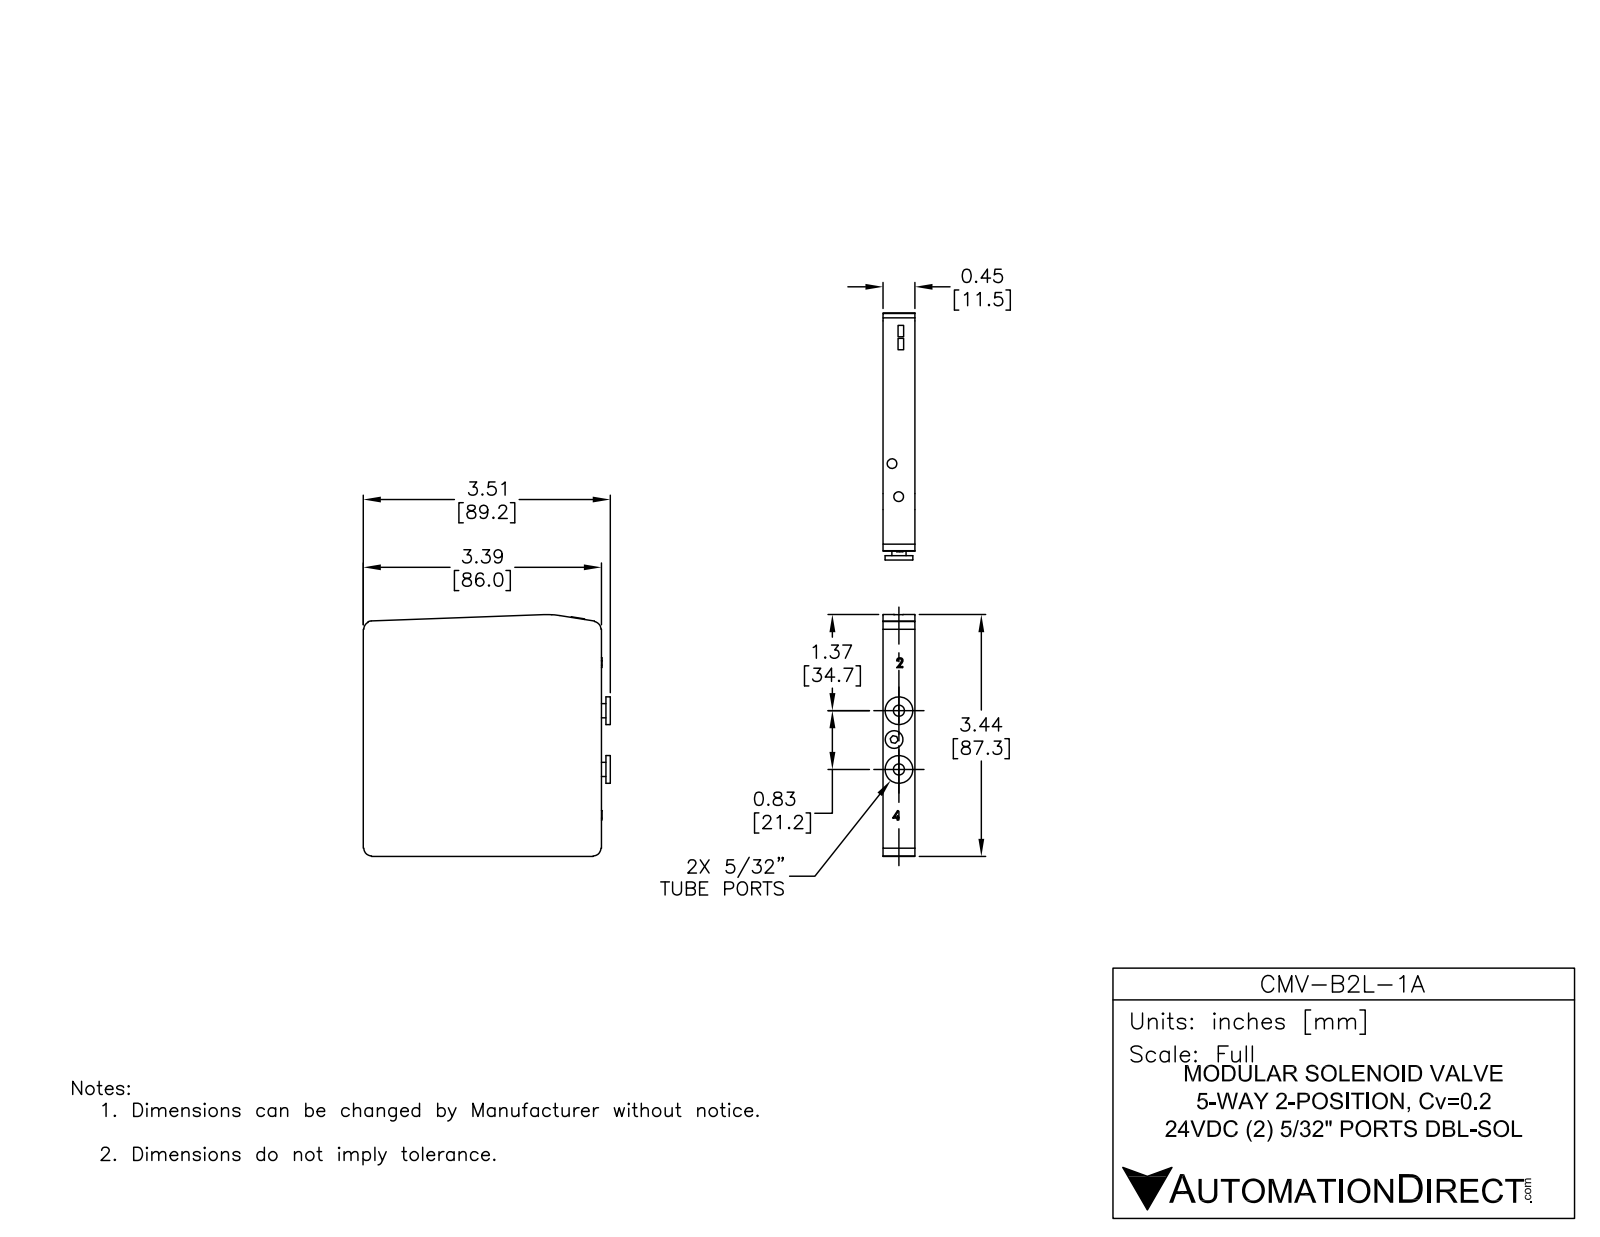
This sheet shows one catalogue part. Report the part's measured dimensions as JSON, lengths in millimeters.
{"part_name": "CMV-B2L-1A", "step_written_by": "SolidWorks 2013 (AUTOMOTIVE_DESIGN)", "units": "millimeters", "bodies": {"solids": 78, "faces": 1147, "planar": 881, "cylindrical": 162, "other": 104}, "overall_size": [89.5, 87.3, 20.43], "volume_mm3": 78068, "surface_area_mm2": 44223, "round_holes": [[5.25, 4], [6.5, 4], [3.35, 2], [4.4, 2], [8, 2], [9.5, 2], [3.6, 1], [6.25, 1], [6.4, 1]], "round_bosses_or_shafts": [[1.5, 4], [10.8, 2], [7.75, 2], [6.25, 2], [5.75, 2], [4.2, 2], [4, 2], [3.5, 1]], "partial_cylinders_radius": [[2.35, 12], [0.78, 4], [1.5, 4], [2.8, 4], [0.15, 2], [0.25, 2], [1, 2], [2.25, 2]], "face_to_face_distances": [11.5, 1.5, 10, 1, 3, 83, 2.5, 12.5, 10.83, 11.83], "hole_center_spacings": [9.7, 19.83, 22.17, 8.66, 8.68, 9.46, 10.38, 10.63]}
